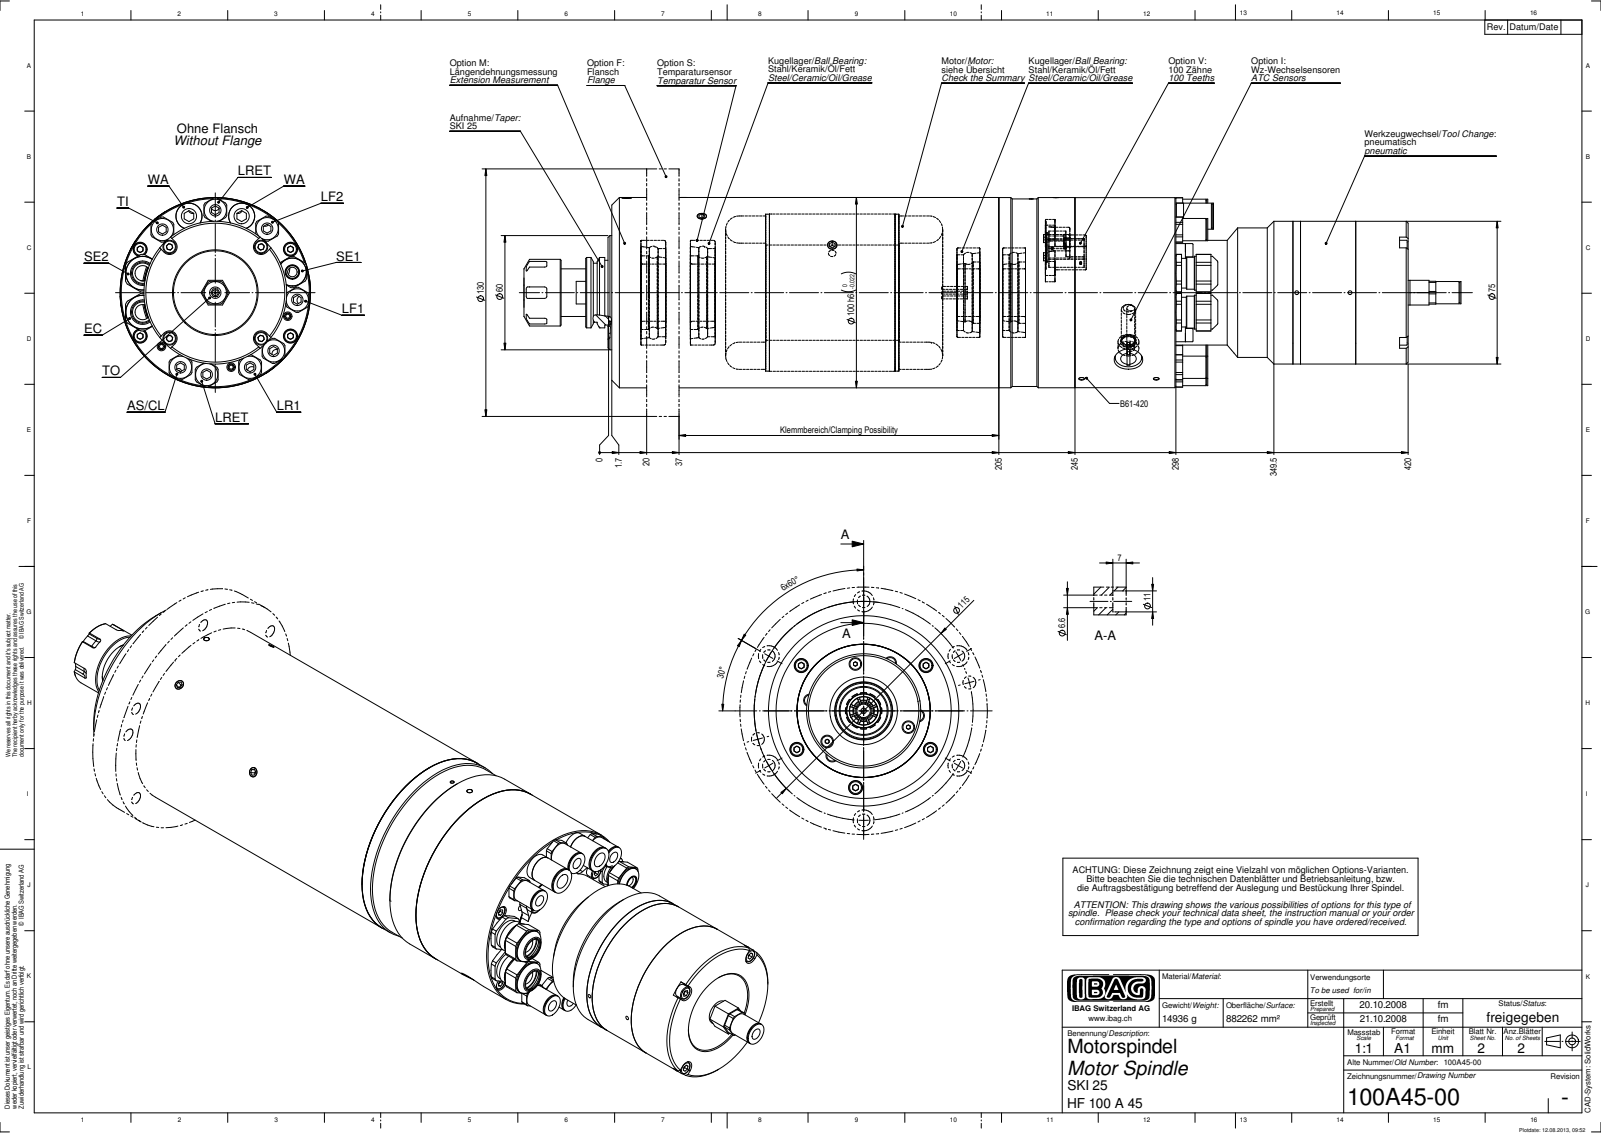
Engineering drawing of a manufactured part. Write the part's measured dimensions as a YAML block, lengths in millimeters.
part_name: "100A45-00"
step_written_by: "SolidWorks 2012 (CONFIG_CONTROL_DESIGN)"
units: millimeters
bodies: {solids: 0, faces: 974, planar: 418, cylindrical: 362, other: 194}
overall_size: [492.24, 100.05, 100]
round_holes:
  - {diameter: 6, count: 9}
  - {diameter: 7.4, count: 9}
  - {diameter: 8, count: 4}
  - {diameter: 2, count: 3}
  - {diameter: 4.5, count: 3}
  - {diameter: 15, count: 3}
  - {diameter: 3.3, count: 2}
  - {diameter: 5, count: 2}
  - {diameter: 10.7, count: 2}
  - {diameter: 16.2, count: 2}
  - {diameter: 6.7, count: 1}
  - {diameter: 10, count: 1}
round_bosses_or_shafts:
  - {diameter: 11.7, count: 9}
  - {diameter: 7, count: 8}
  - {diameter: 5.7, count: 6}
  - {diameter: 10.53, count: 3}
  - {diameter: 17.8, count: 2}
  - {diameter: 16.79, count: 2}
  - {diameter: 15.59, count: 2}
  - {diameter: 13.7, count: 2}
partial_cylinders:
  - {radius: 1, count: 12}
  - {radius: 6.6, count: 9}
  - {radius: 5, count: 8}
  - {radius: 4, count: 4}
  - {radius: 9.9, count: 2}
  - {radius: 8.25, count: 1}
  - {radius: 14.5, count: 1}
face_to_face_distances: [118.5, 361.8, 243.3, 53, 296.3, 65.5, 357.8, 114.5, 61.5, 4]
hole_center_spacings: [43.25, 45.6, 26.81, 38.1, 40, 40.5, 72.27, 79.5]
